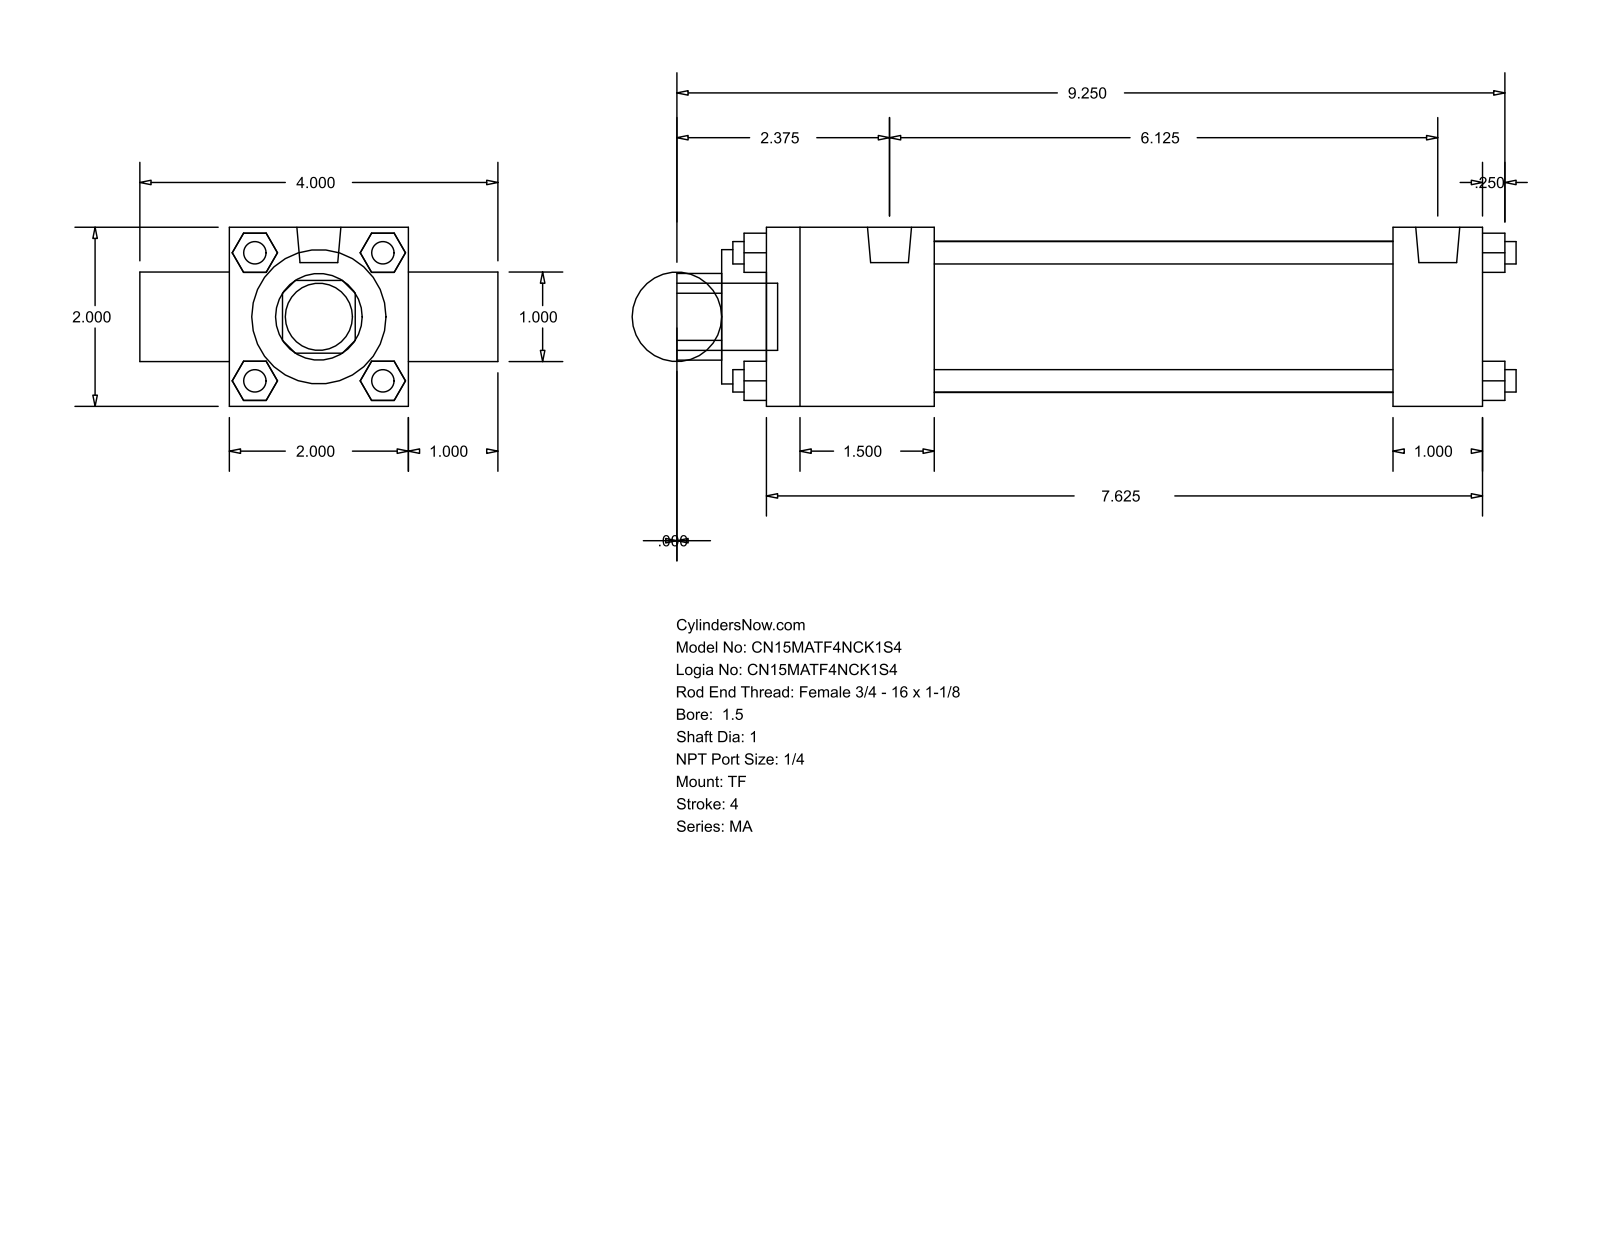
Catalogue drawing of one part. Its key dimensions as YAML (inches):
part_name: "MA_TF__0150_1"
step_written_by: "GSSL Pune (CONFIG_CONTROL_DESIGN)"
units: inches
bodies: {solids: 0, faces: 120, planar: 92, cylindrical: 28, other: 0}
overall_size: [9.375, 4, 2]
round_holes:
  - {diameter: 1, count: 2}
  - {diameter: 1.5, count: 1}
  - {diameter: 1.69, count: 1}
round_bosses_or_shafts:
  - {diameter: 0.25, count: 4}
  - {diameter: 0.313, count: 3}
  - {diameter: 0.492, count: 2}
  - {diameter: 0.75, count: 1}
partial_cylinders:
  - {radius: 0.484, count: 1}
face_to_face_distances: [2, 1, 8, 3, 0.25, 1.875, 7, 5.125, 6.125, 8.5]
